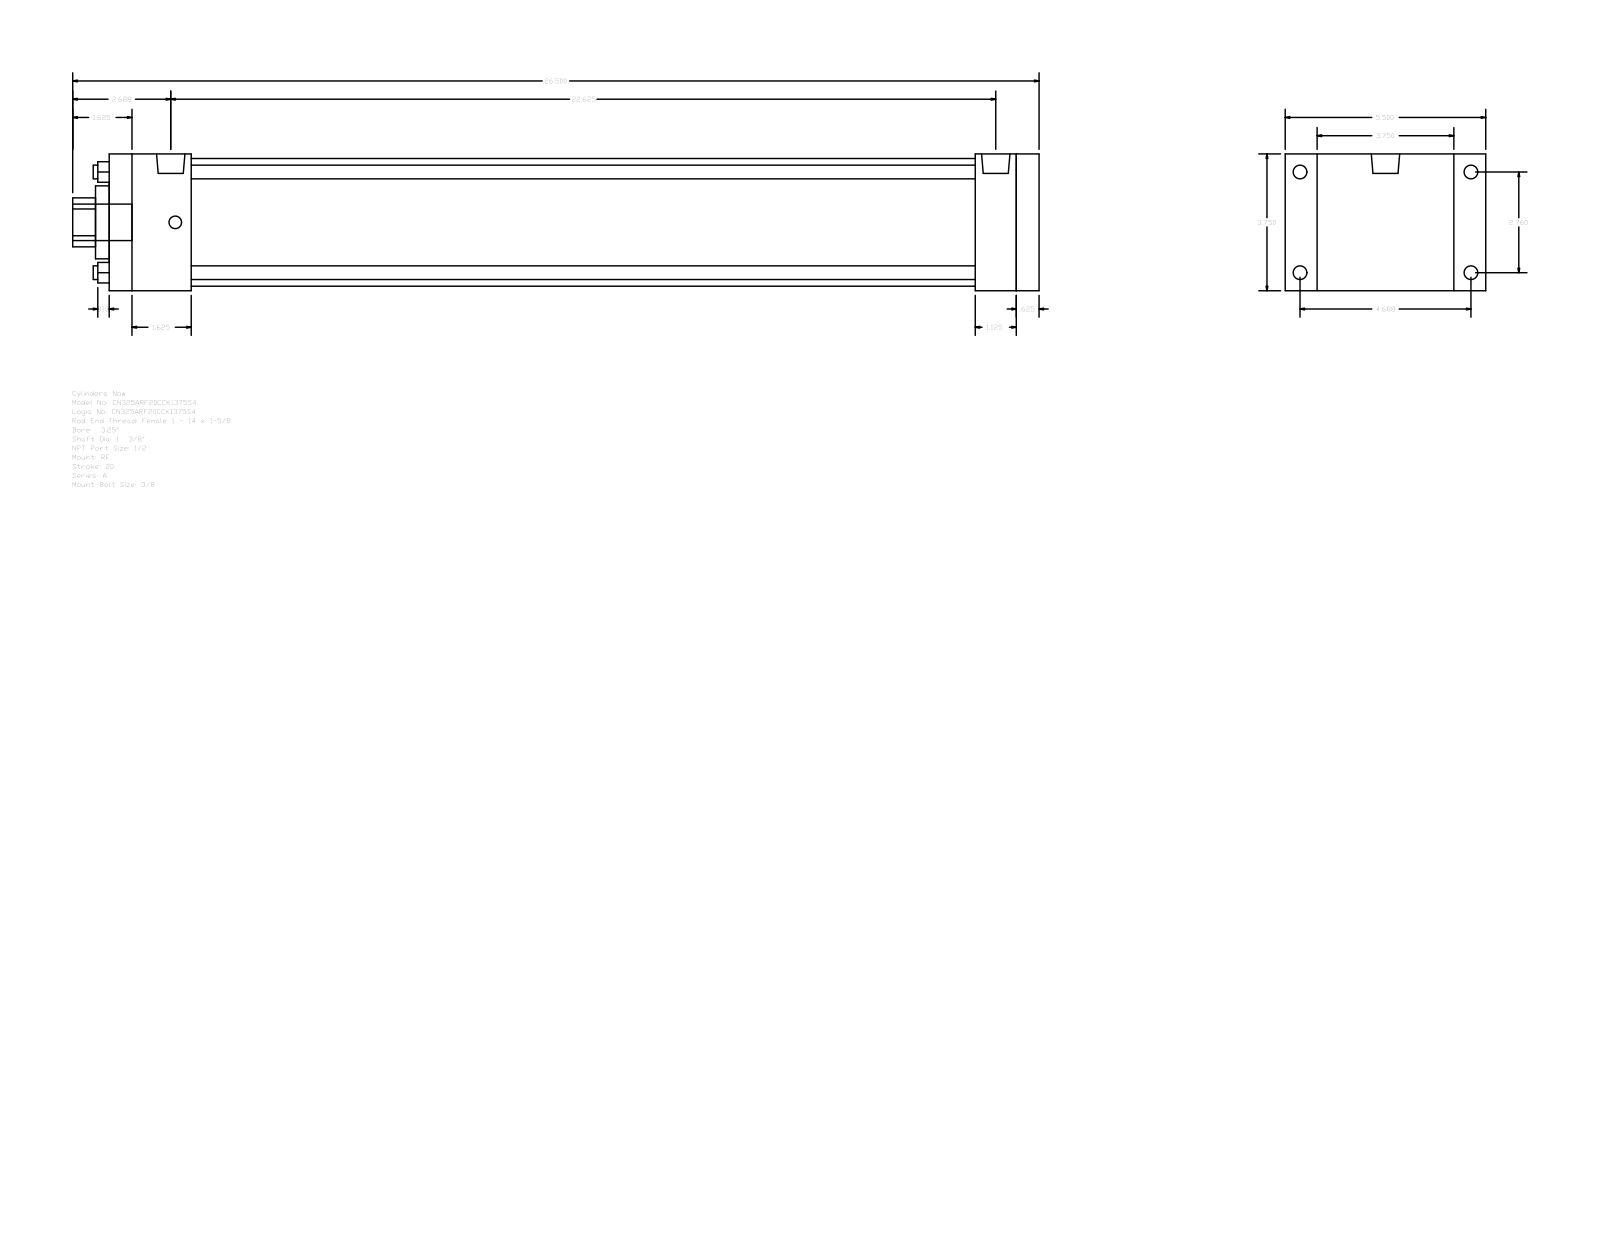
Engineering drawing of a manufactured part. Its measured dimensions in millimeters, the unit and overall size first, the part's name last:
Units: millimetres
Overall size (bounding box): 673.1 × 139.7 × 95.25
Round holes (diameter × count): ⌀9.53 ×4, ⌀34.92 ×1, ⌀50.8 ×1, ⌀88.9 ×1
Round bosses / shafts (diameter × count): ⌀9.53 ×4, ⌀8.73 ×4, ⌀19.77 ×2, ⌀25.4 ×1
Partial cylindrical surfaces — rounded edges, fillets, slot ends (radius × count): R17.06 ×1
Main face-to-face distances: 95.24, 647.7, 15.87, 631.83, 28.58, 22.23, 117.47, 603.25, 44.45, 57.15
Hole centre spacings: 49.57, 70.1, 99.14
Bodies: 0 solids, 92 faces (64 planar, 28 cylindrical, 0 other)
Part name (STEP PRODUCT): A_RF__0325_1.375
STEP written by: GSSL Pune (CONFIG_CONTROL_DESIGN)
